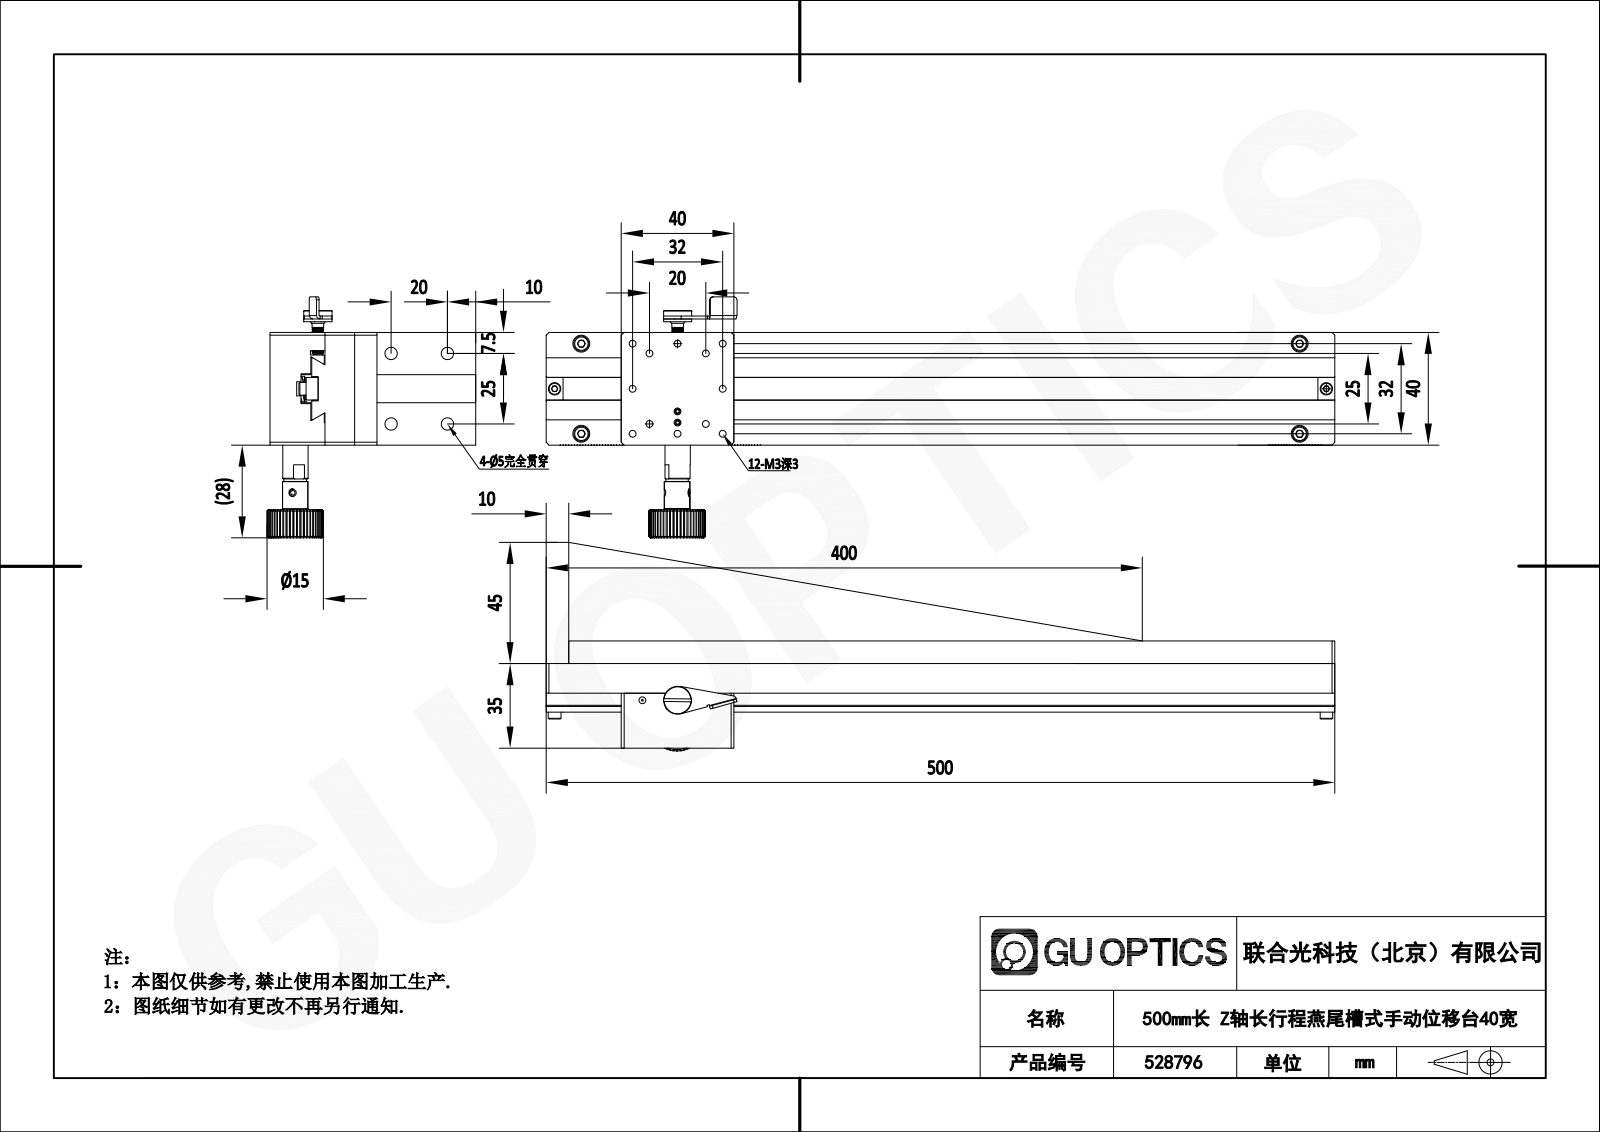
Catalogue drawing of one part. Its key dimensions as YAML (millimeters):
part_name: "528796"
step_written_by: "SolidWorks 2020 (CONFIG_CONTROL_DESIGN)"
units: millimeters
bodies: {solids: 41, faces: 1452, planar: 774, cylindrical: 319, other: 359}
overall_size: [500, 85.49, 80]
volume: 544865
surface_area: 162045
round_holes:
  - {diameter: 2.5, count: 32}
  - {diameter: 3.3, count: 23}
  - {diameter: 6, count: 18}
  - {diameter: 2.9, count: 9}
  - {diameter: 4.5, count: 9}
  - {diameter: 2.05, count: 8}
  - {diameter: 5, count: 7}
  - {diameter: 8, count: 5}
  - {diameter: 4, count: 1}
  - {diameter: 4.1, count: 1}
round_bosses_or_shafts:
  - {diameter: 3, count: 10}
  - {diameter: 5.5, count: 8}
  - {diameter: 2.5, count: 8}
  - {diameter: 4.5, count: 7}
  - {diameter: 4, count: 5}
  - {diameter: 7, count: 4}
  - {diameter: 9, count: 2}
  - {diameter: 10, count: 1}
partial_cylinders:
  - {radius: 1.05, count: 8}
  - {radius: 1, count: 3}
  - {radius: 2.5, count: 2}
  - {radius: 0.2, count: 1}
  - {radius: 1.2, count: 1}
  - {radius: 10, count: 1}
face_to_face_distances: [10, 15, 25, 20.5, 10.5, 40, 22.9, 12.9, 2.4, 2.3]
hole_center_spacings: [32, 50, 59.36, 16, 100, 105, 35.78, 150]
